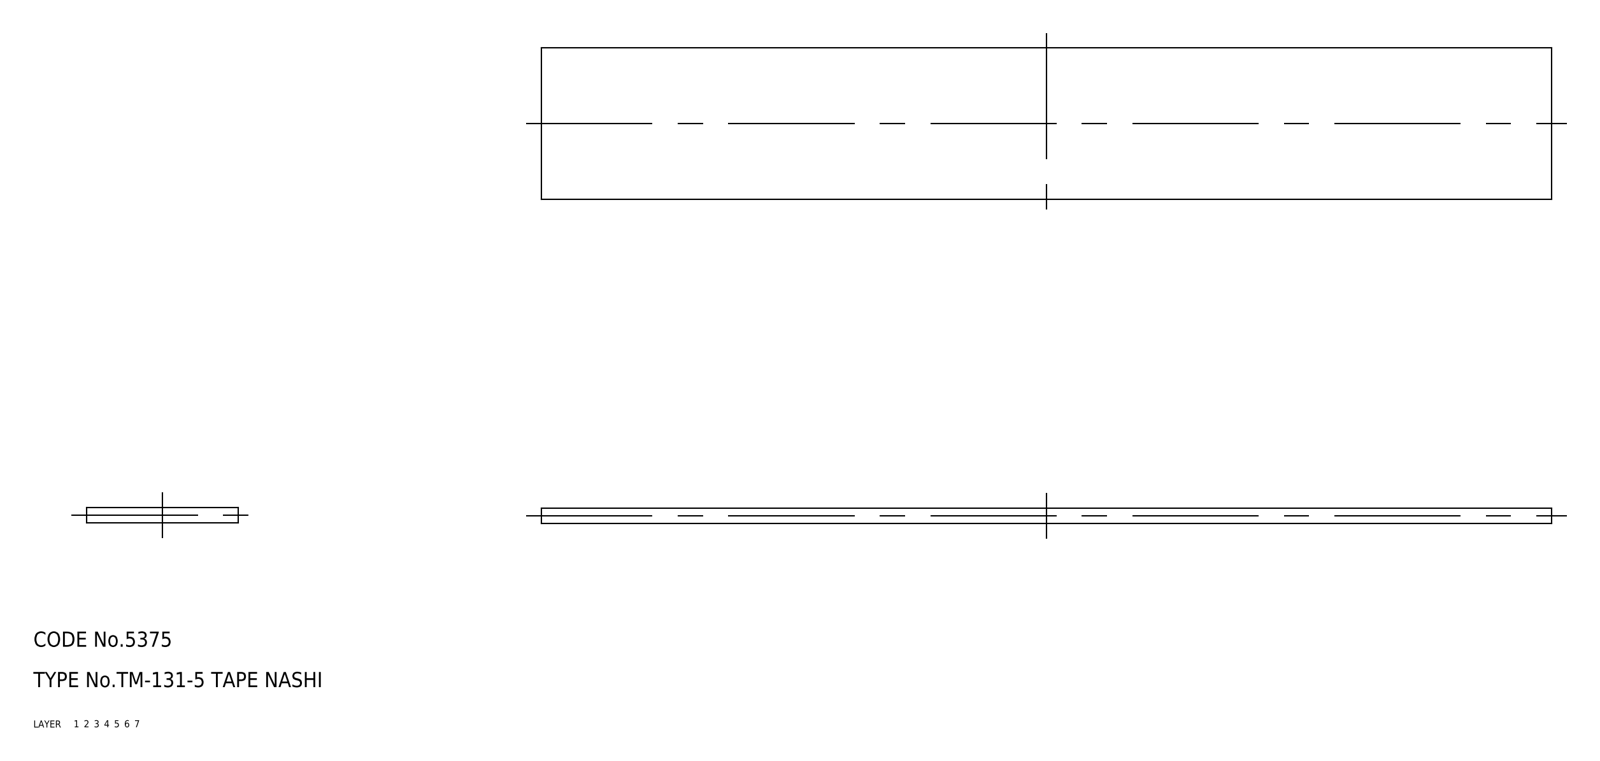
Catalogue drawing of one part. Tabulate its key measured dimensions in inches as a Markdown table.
| quantity | value |
| --- | --- |
| part name | rubber foam |
| STEP written by | CADfix (AUTOMOTIVE_DESIGN) |
| units | inches |
| bodies | 1 solid, 6 faces (0 planar, 0 cylindrical, 6 other) |
| overall size | 7.874 × 1.181 × 0.118 |
| volume | 1.098 in³ |
| surface area | 20.74 in² |
